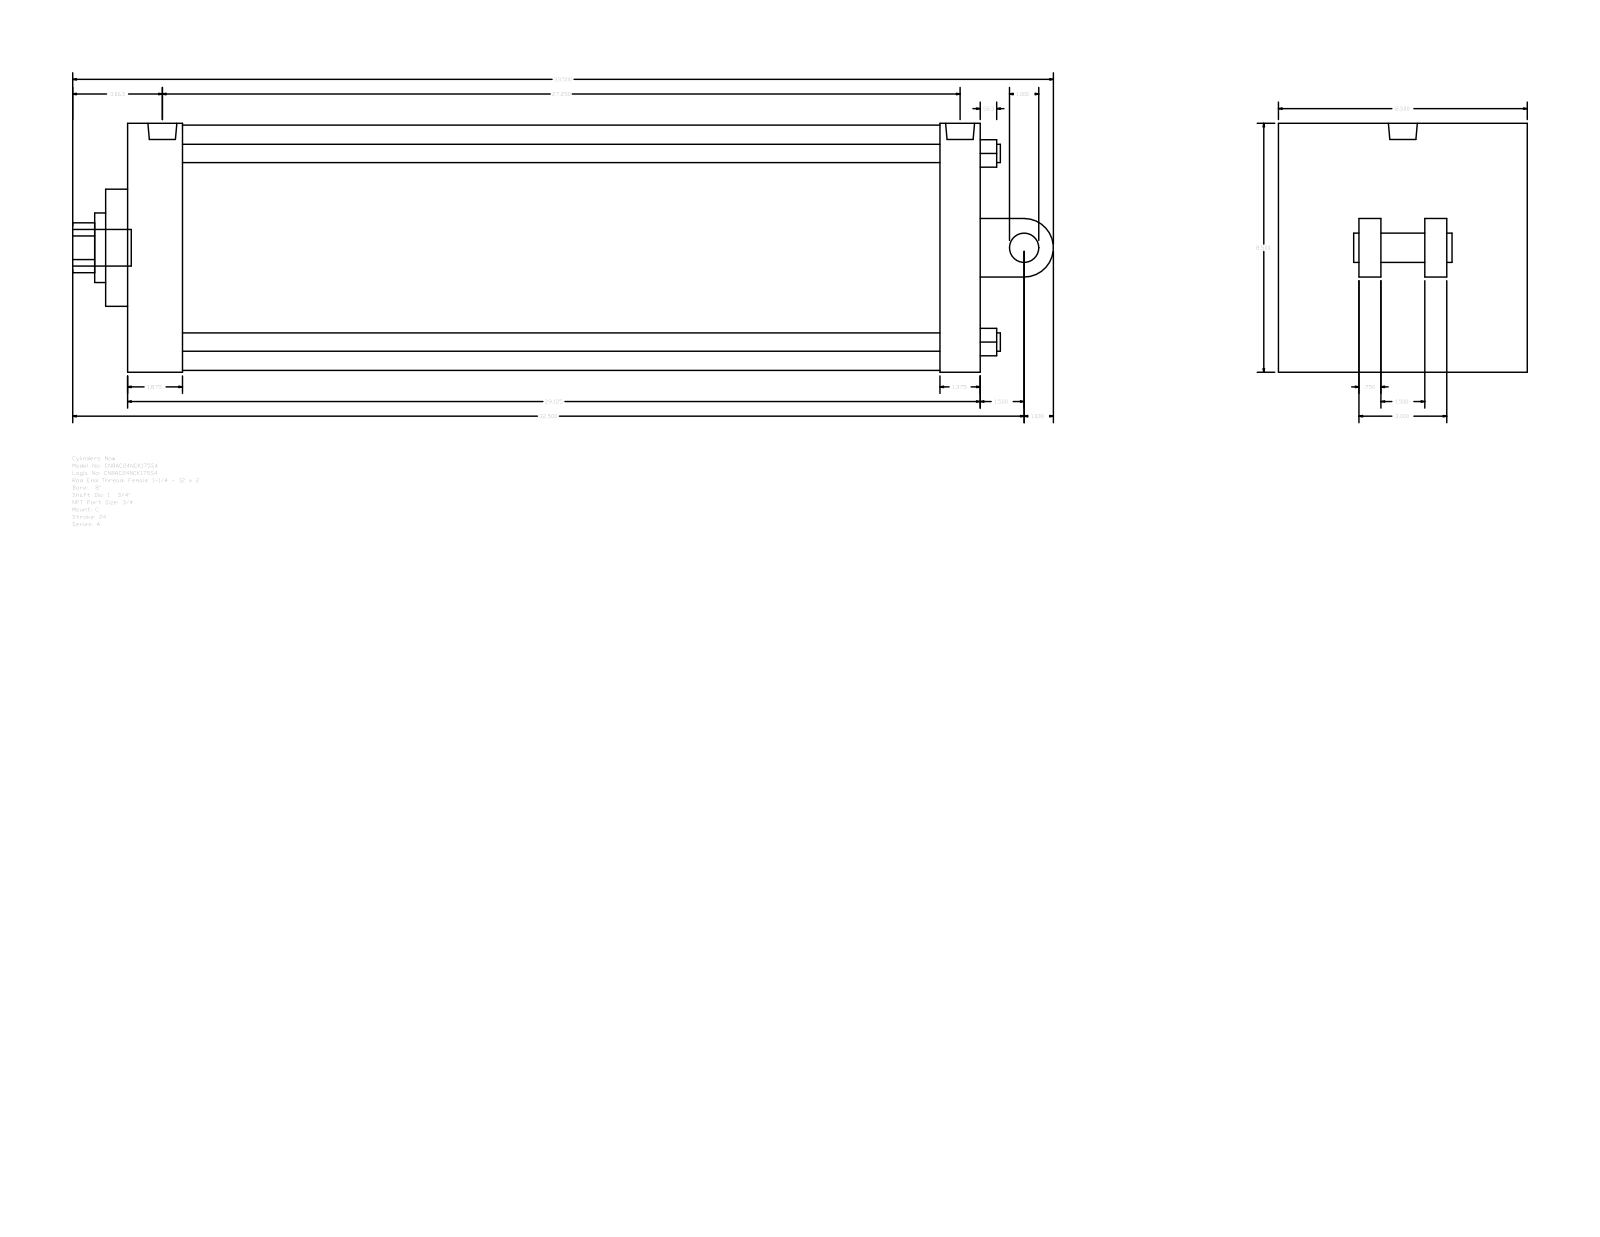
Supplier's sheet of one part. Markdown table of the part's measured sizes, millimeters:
| quantity | value |
| --- | --- |
| part name | A_C__0800_1.75 |
| STEP written by | GSSL Pune (CONFIG_CONTROL_DESIGN) |
| units | millimeters |
| bodies | 0 solids, 104 faces (75 planar, 29 cylindrical, 0 other) |
| overall size | 850.9 × 215.9 × 215.9 |
| round holes (diameter × count) | 15.88 × 4, 15.08 × 2, 25.12 × 1, 44.45 × 1, 60.33 × 1, 212.72 × 1 |
| round bosses / shafts (diameter × count) | 15.08 × 2, 31.75 × 1, 25.4 × 1, 25.12 × 1 |
| partial cylindrical surfaces (radius × count) | 21.63 × 1, 25.4 × 1 |
| main face-to-face distances | 739.78, 215.9, 19.05, 57.15, 34.92, 47.63, 692.15, 704.86, 657.23, 88.9 |
| hole center spacings | 115.67, 163.58, 231.34, 6.35 |
